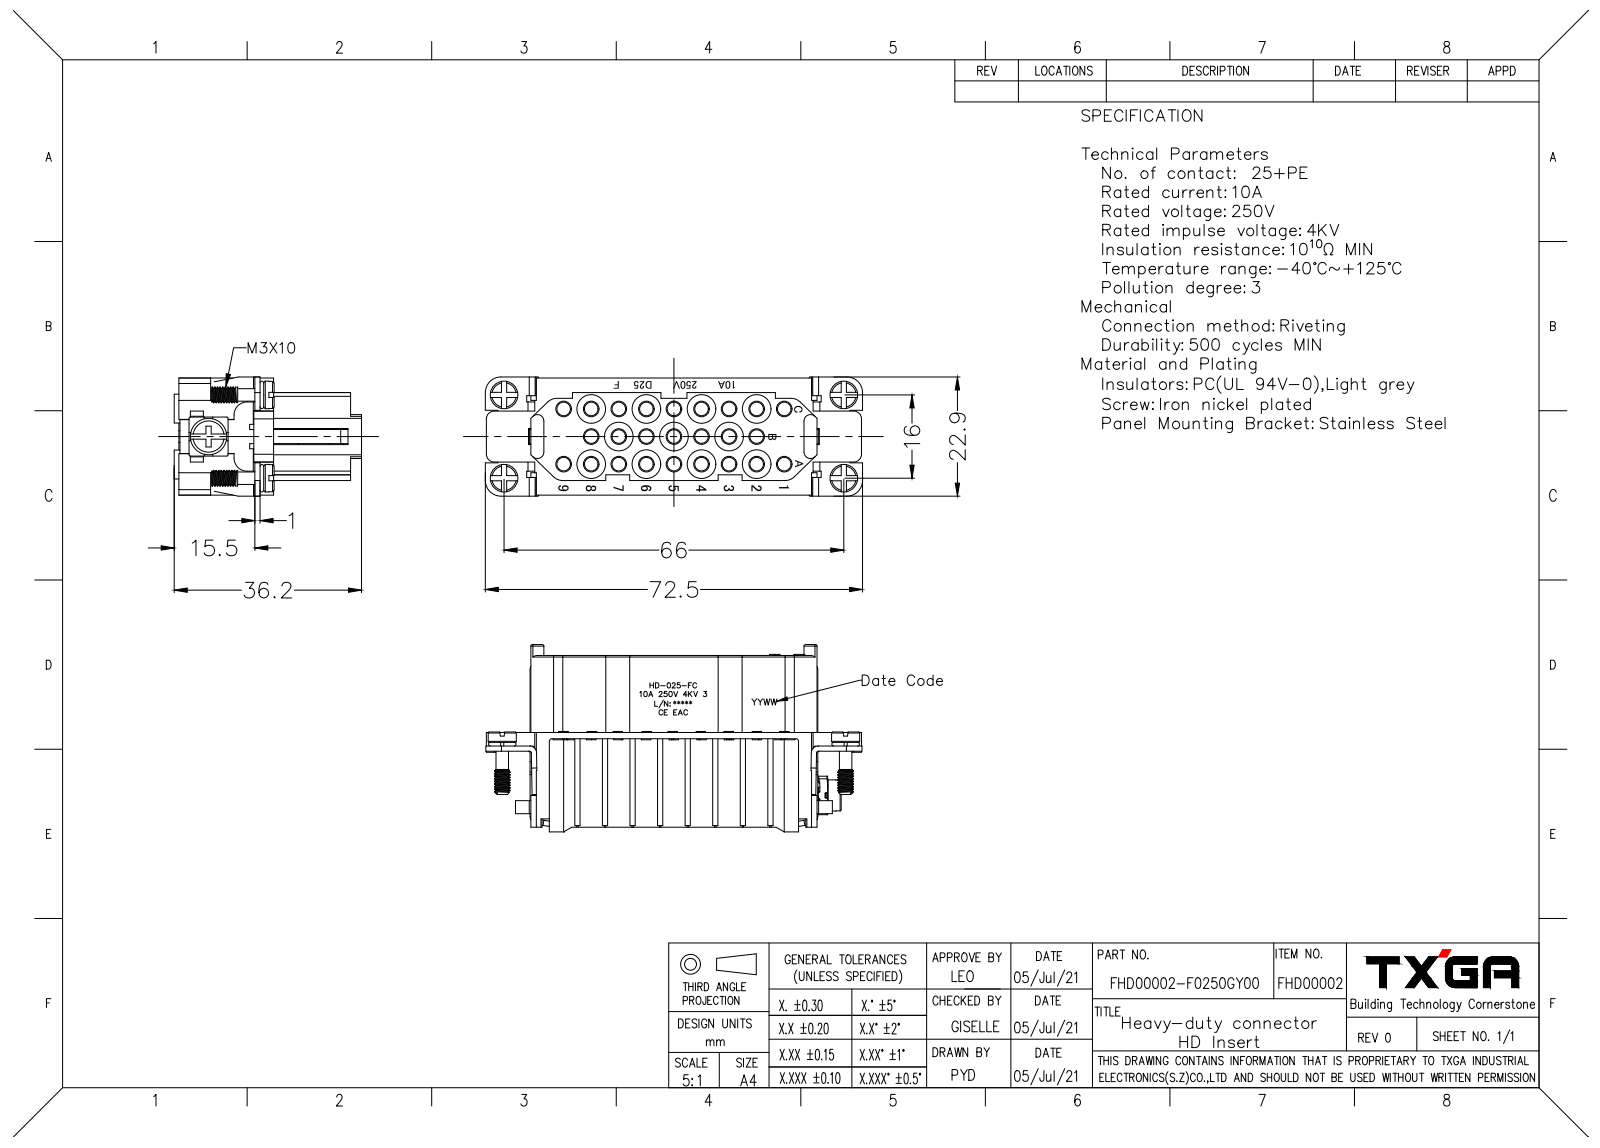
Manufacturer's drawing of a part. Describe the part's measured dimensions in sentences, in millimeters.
The part is named "FHD00002-F0250GY00 HD-025-FC-REF（渲染）". Its 3-D file was written by "SolidWorks 2021 (CONFIG_CONTROL_DESIGN)". It is 1 solid with 1044 faces: 464 planar, 448 cylindrical and 132 other. Overall it measures 72.5 by 36.2 by 22.9 millimeters. Its volume is 20 936 cubic millimeters and its surface area 23 982 square millimeters. Round holes: 29 of diameter 3, 29 of diameter 4, 12 of diameter 1.34, 11 of diameter 4.9, 1 of diameter 2.8, 1 of diameter 3.1. Round bosses or shafts: 5 of diameter 6, 5 of diameter 2.6. Partial cylindrical surfaces (rounded edges, fillets, slot ends): 32 of radius 0.5, 14 of radius 2.44, 12 of radius 1.2, 10 of radius 1, 8 of radius 0.2, 8 of radius 2, 8 of radius 3, 4 of radius 2.55. The main face-to-face distances are 1, 5.5, 11, 16.5, 22, 4.5, 17.5, 6.5, 10, 12. The hole center spacings are 5.5, 11, 3.55, 3.89, 8.22, 8.55, 11.32, 7.43.
